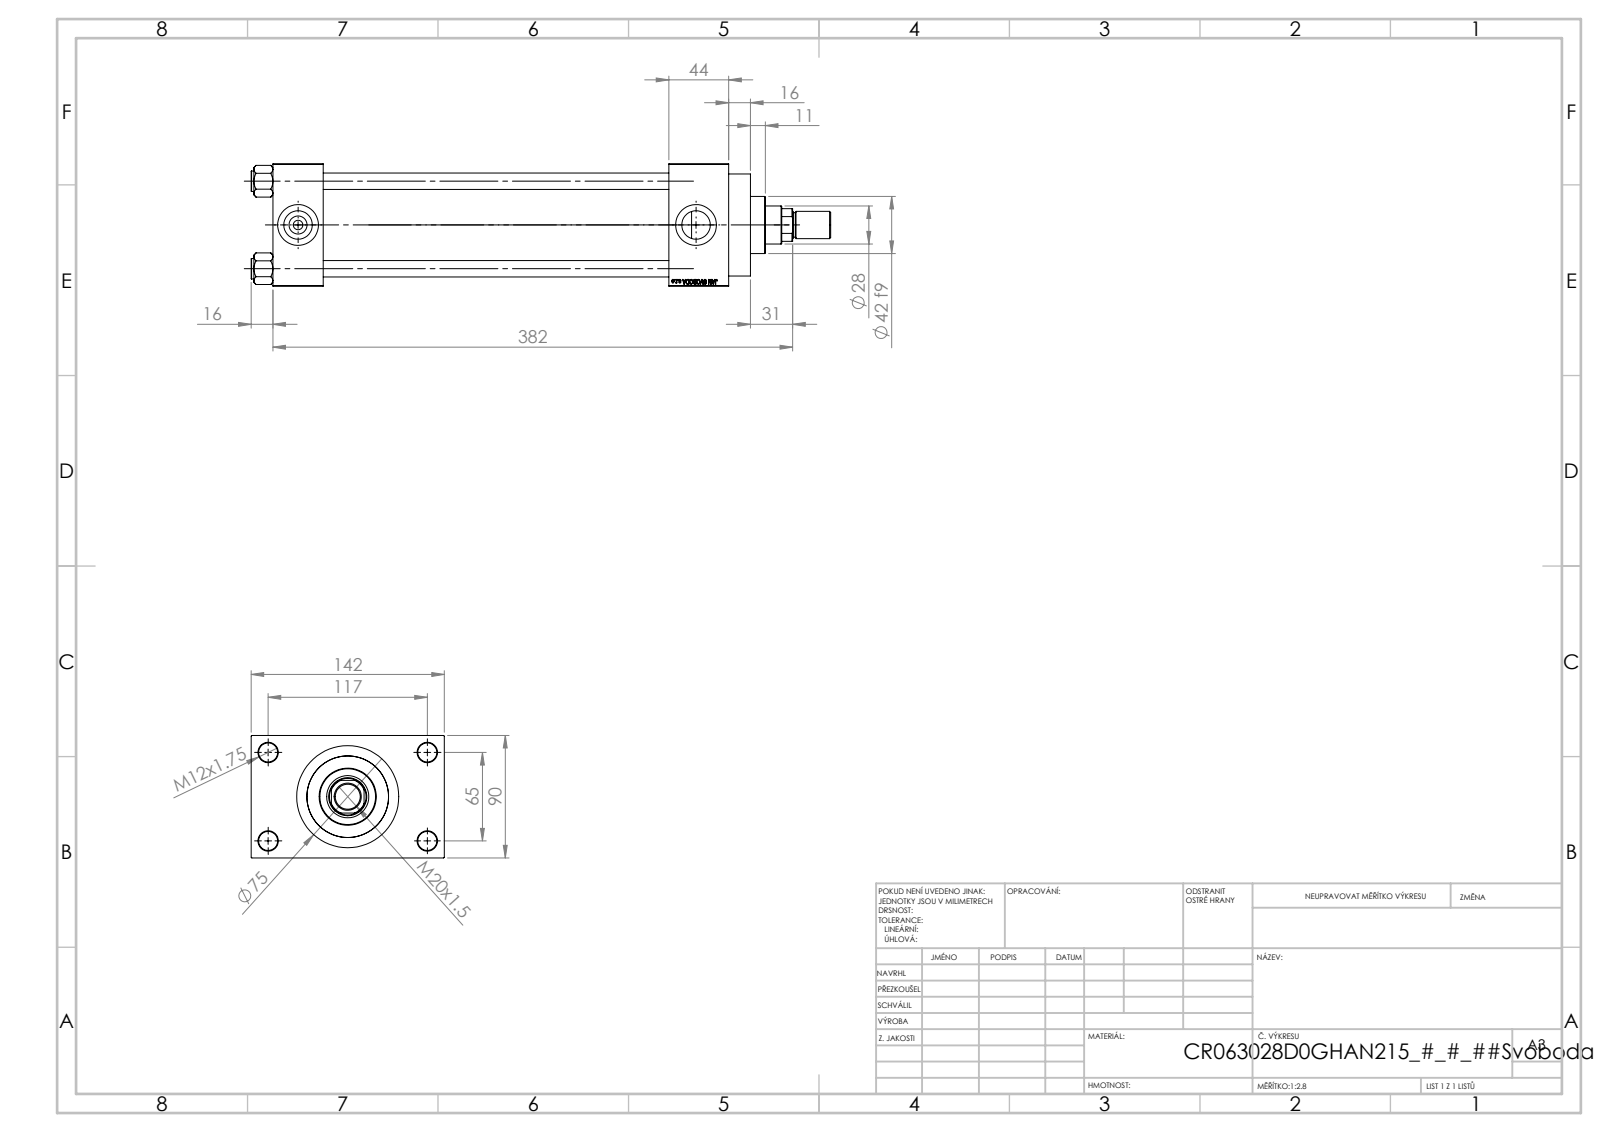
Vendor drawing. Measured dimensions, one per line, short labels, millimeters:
name: NUT_M5_D; V215CR_VCP_D; ROD_END_AH; V215_VC_A (+2 more)
written by: SolidWorks 2019 (CONFIG_CONTROL_DESIGN)
unit: mm
bodies: 12 solids, 1117 faces (501 planar, 92 cylindrical, 524 other)
size: 426 × 142 × 90
volume: 1 435 000 mm³; area: 330 170 mm²
holes: 4× ⌀12, 4× ⌀14, 2× ⌀7, 2× ⌀20.96, 2× ⌀30, 1× ⌀18.5, 1× ⌀28, 1× ⌀31, 1× ⌀50, 1× ⌀60, 1× ⌀63
bosses: 4× ⌀15, 1× ⌀75, 1× ⌀69, 1× ⌀42, 1× ⌀20, 1× ⌀18
rounds: 1× R13.5
face distances: 90, 254, 37, 291, 298, 335, 44, 26, 116, 16
hole spacings: 26.35, 45.47, 64.3, 66.92, 69.81, 90.65, 111.34, 65
